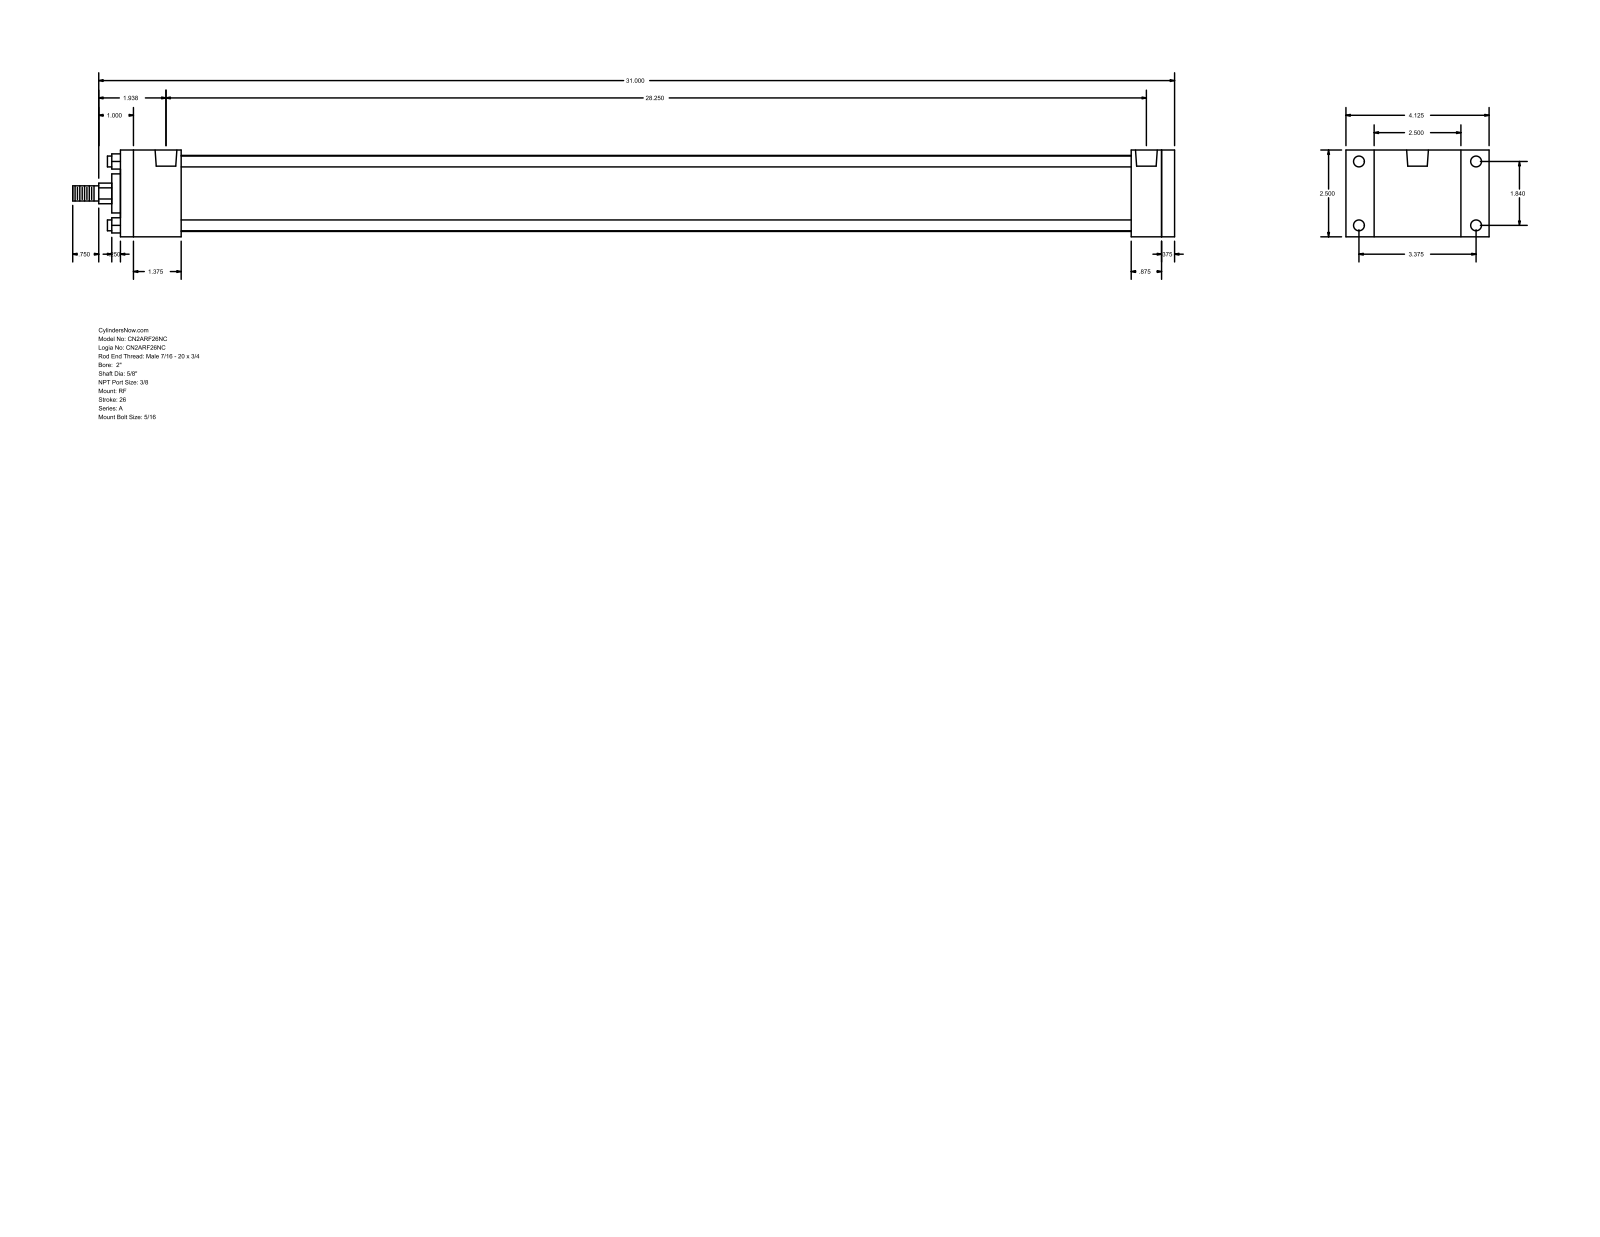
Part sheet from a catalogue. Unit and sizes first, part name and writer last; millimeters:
Units: millimetres
Overall size (bounding box): 806.45 × 104.78 × 63.5
Round holes (diameter × count): ⌀5.56 ×4, ⌀7.94 ×4, ⌀15.93 ×2
Round bosses / shafts (diameter × count): ⌀7.94 ×4, ⌀55.63 ×1, ⌀28.57 ×1, ⌀15.88 ×1, ⌀11.11 ×1
Partial cylindrical surfaces — rounded edges, fillets, slot ends (radius × count): R7.54 ×1
Main face-to-face distances: 63.5, 771.52, 762, 9.52, 44.45, 717.55, 727.07, 739.77, 695.32, 22.23
Hole centre spacings: 46.74, 85.72, 97.63, 709.6, 3.97, 3.98, 713.57, 713.58
Bodies: 0 solids, 92 faces (64 planar, 28 cylindrical, 0 other)
Part name (STEP PRODUCT): A_RF__0200_0.625
STEP written by: GSSL Pune (CONFIG_CONTROL_DESIGN)
